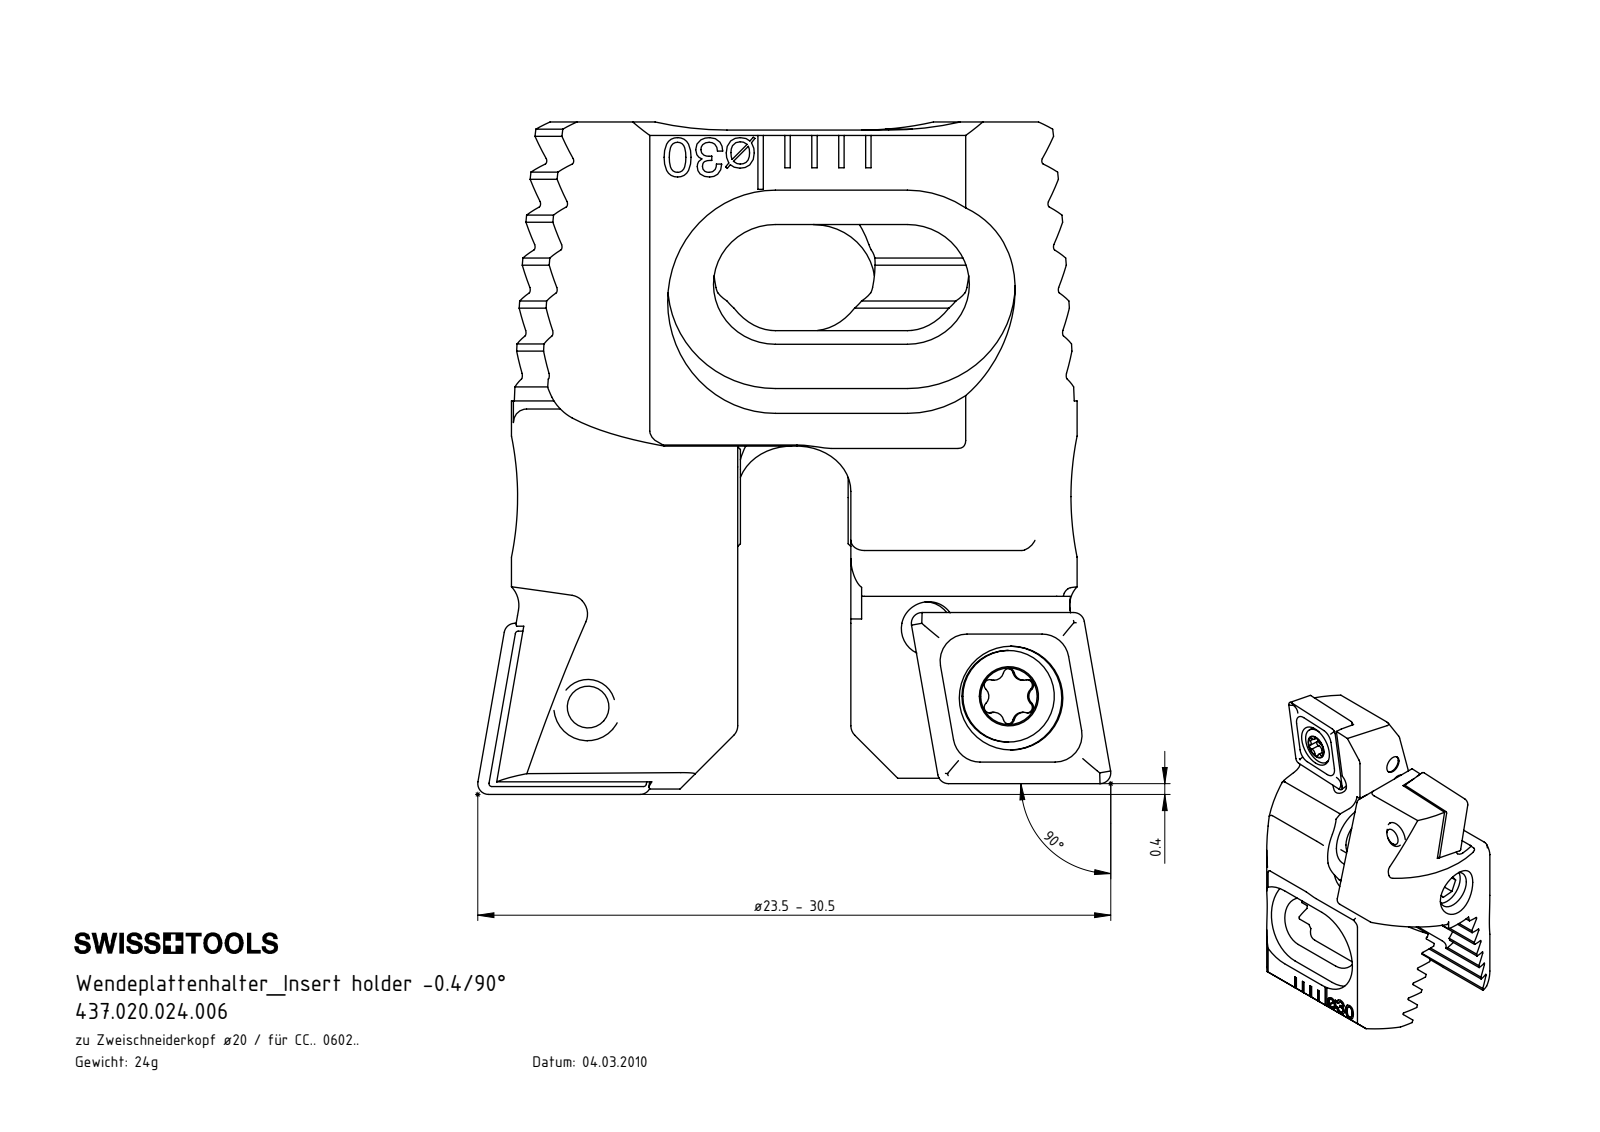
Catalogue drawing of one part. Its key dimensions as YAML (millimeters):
part_name: "CCMT060204; Z20-xxx.001.015_D; Z20-ER3.001.007_A; Z20-WCA.004.015 (+2 more)"
step_written_by: "SolidWorks 2015 (AUTOMOTIVE_DESIGN)"
units: millimeters
bodies: {solids: 8, faces: 613, planar: 262, cylindrical: 137, other: 214}
overall_size: [24.95, 23.5, 16.2]
volume: 2944
surface_area: 3407
round_holes:
  - {diameter: 1.6, count: 4}
  - {diameter: 2, count: 2}
  - {diameter: 2.05, count: 2}
  - {diameter: 2.8, count: 2}
  - {diameter: 3.85, count: 2}
  - {diameter: 3.5, count: 1}
  - {diameter: 9.1, count: 1}
round_bosses_or_shafts:
  - {diameter: 3.4, count: 2}
  - {diameter: 2.5, count: 2}
  - {diameter: 4, count: 1}
partial_cylinders:
  - {radius: 0.5, count: 16}
  - {radius: 0.12, count: 12}
  - {radius: 0.21, count: 12}
  - {radius: 0.36, count: 10}
  - {radius: 2, count: 4}
  - {radius: 2.3, count: 4}
  - {radius: 4, count: 4}
  - {radius: 12, count: 4}
face_to_face_distances: [1.43, 2.86, 4.29, 3.79, 0.4, 4.6, 5.71, 5.72, 2.97, 6.76]
hole_center_spacings: [2.5, 3.91, 4.01, 5.5, 15.99, 5, 6.05, 7.43]
